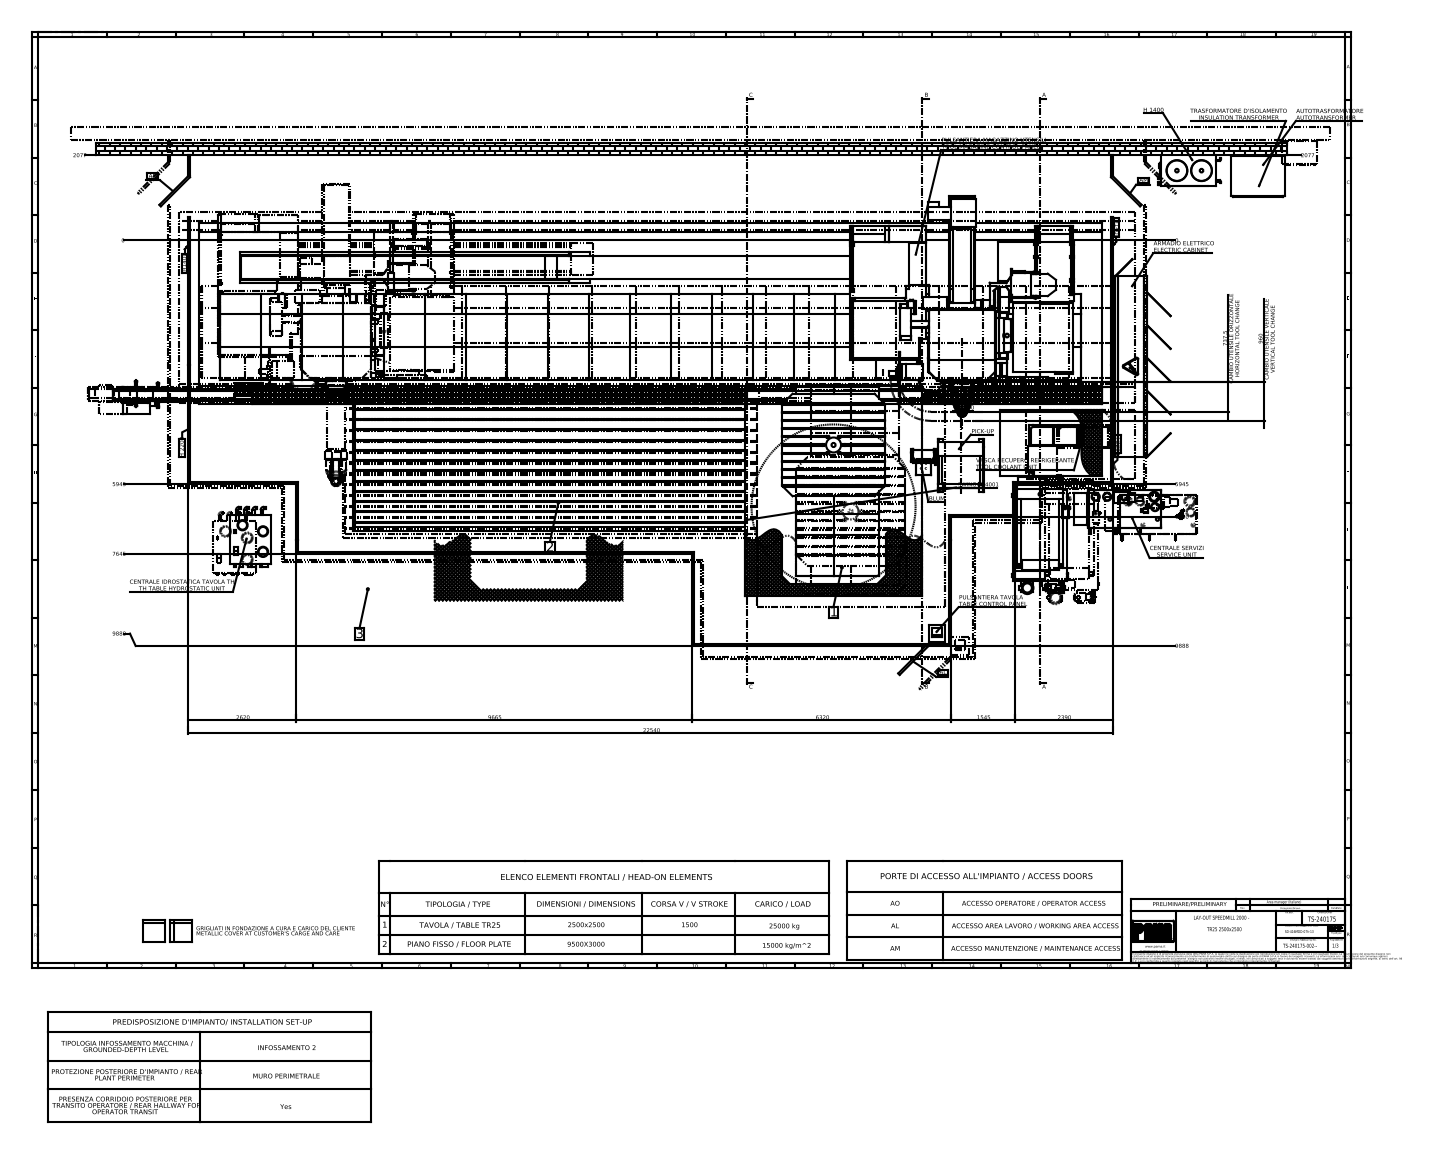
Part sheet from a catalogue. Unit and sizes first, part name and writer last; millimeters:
Units: millimetres
Overall size (bounding box): 29040 × 15215 × 9400
Round holes (diameter × count): ⌀35 ×152, ⌀69.6 ×83, ⌀14 ×8, ⌀8 ×6, ⌀32 ×6, ⌀12 ×4, ⌀30 ×4, ⌀50 ×3, ⌀19 ×2, ⌀81 ×2, ⌀85 ×2, ⌀100 ×2
Round bosses / shafts (diameter × count): ⌀55 ×8, ⌀30 ×8, ⌀60 ×7, ⌀35 ×6, ⌀200 ×4, ⌀50 ×4, ⌀36 ×4, ⌀28 ×4
Partial cylindrical surfaces — rounded edges, fillets, slot ends (radius × count): R5 ×243, R6 ×36, R15 ×31, R35 ×24, R10 ×23, R20 ×22, R24 ×14, R40 ×13
Main face-to-face distances: 2000, 300, 50, 1340, 660, 15215, 14915, 80, 580, 1950
Hole centre spacings: 250, 500, 750, 1000, 1250, 1500, 1750, 2000
Volume: 896 200 000 000 mm³ · Surface area: 2 856 000 000 mm²
Bodies: 507 solids, 7965 faces (5706 planar, 1587 cylindrical, 672 other)
Part name (STEP PRODUCT): S003544_Y=3500; S001725_DRW6 (A = 0°); S003542_X=MIN; Y=MIN; Z=MIN; W=MIN; S003172 (+8 more)
STEP written by: SolidWorks 2023 (AUTOMOTIVE_DESIGN)
